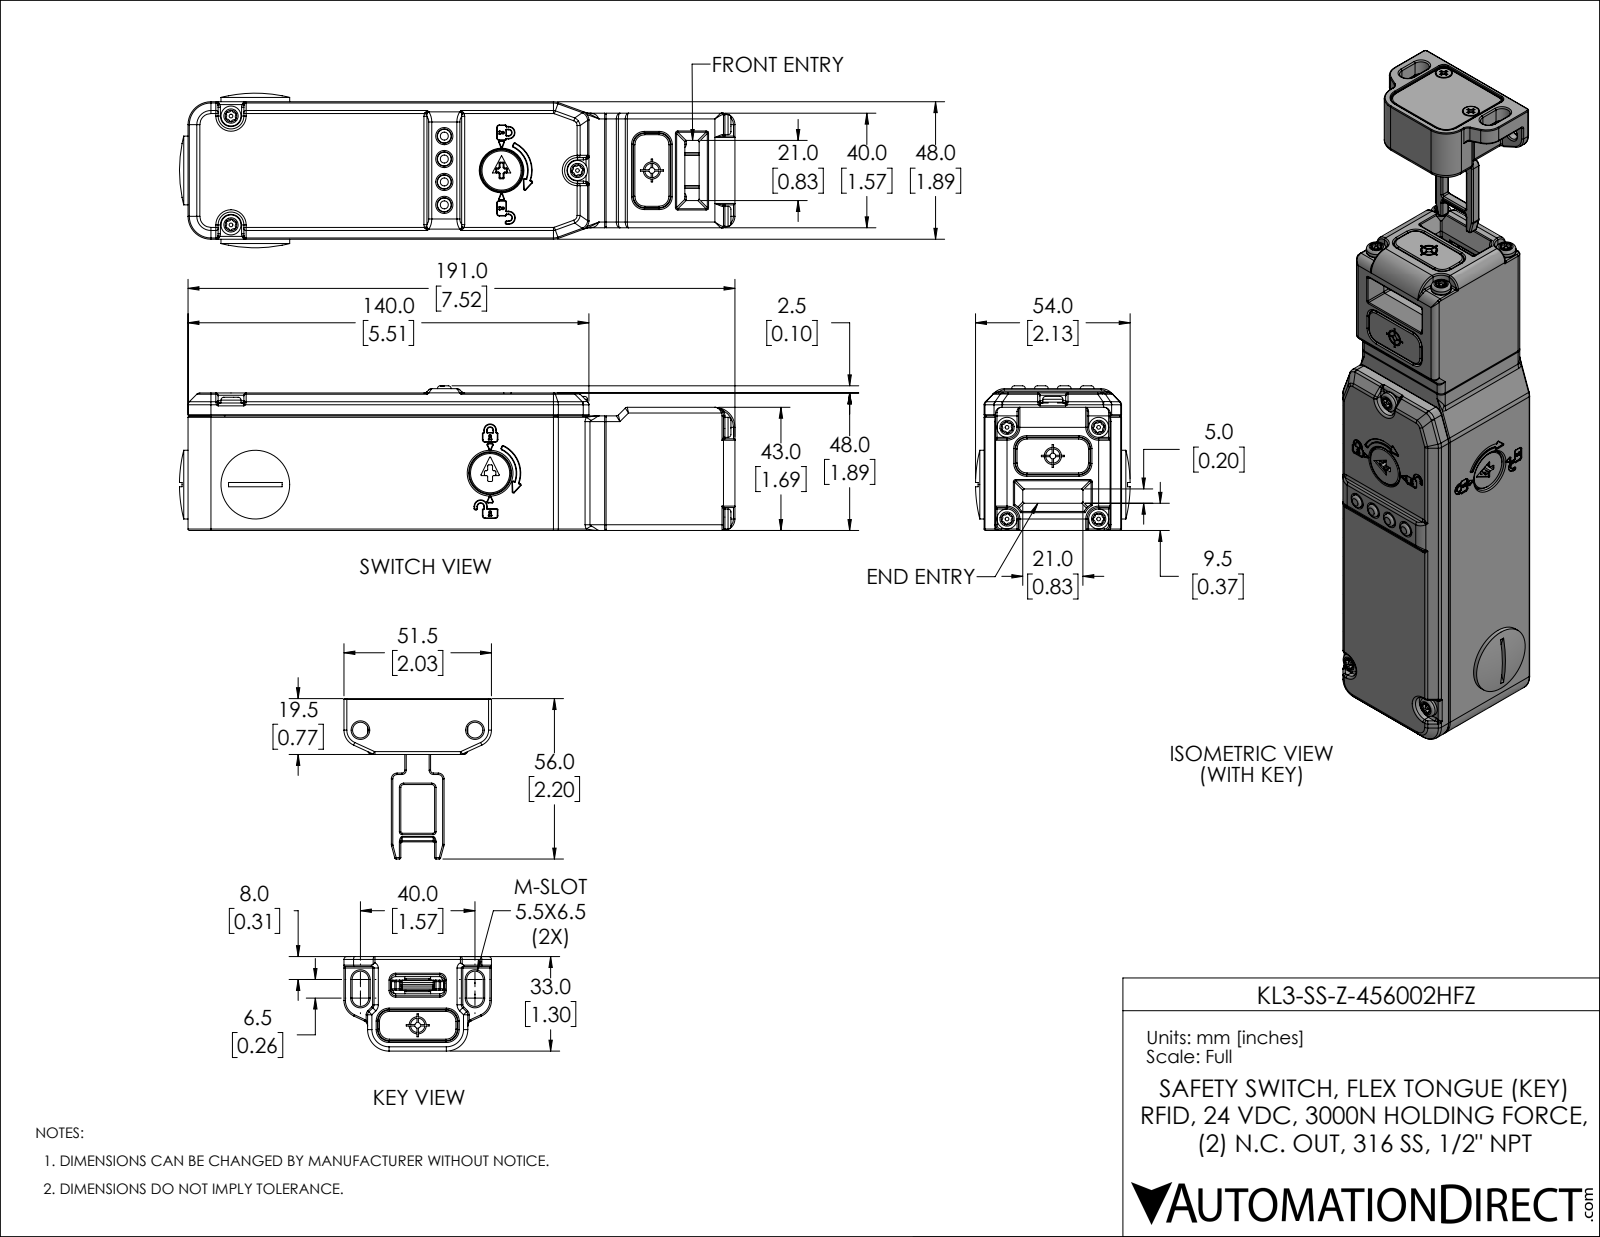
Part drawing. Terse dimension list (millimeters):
name: 456-KL3-SS-Z-HFZ
written by: SolidWorks 2019 (AUTOMOTIVE_DESIGN)
unit: mm
bodies: 28 solids, 3556 faces (945 planar, 1474 cylindrical, 1137 other)
size: 255 × 54 × 50.5
volume: 347 200 mm³; area: 101 300 mm²
holes: 7× ⌀4, 7× ⌀4.5, 6× ⌀2.5, 6× ⌀6, 4× ⌀3.3, 4× ⌀5, 4× ⌀8, 4× ⌀9.3, 3× ⌀4.4, 2× ⌀3.5, 2× ⌀5.5, 2× ⌀14
bosses: 11× ⌀3.5, 7× ⌀7, 7× ⌀1.3, 6× ⌀4.8, 5× ⌀5, 4× ⌀5.5, 4× ⌀2.8, 4× ⌀1
rounds: 476× R0.5, 139× R0.3, 134× R1, 120× R0.2, 52× R2, 35× R1.5, 33× R4, 28× R0.4
face distances: 48, 40, 8, 4, 44, 2.5, 5.5, 45.5, 2, 3.2
hole spacings: 8.1, 10, 12.2, 16, 19, 26.5, 26.5, 32
